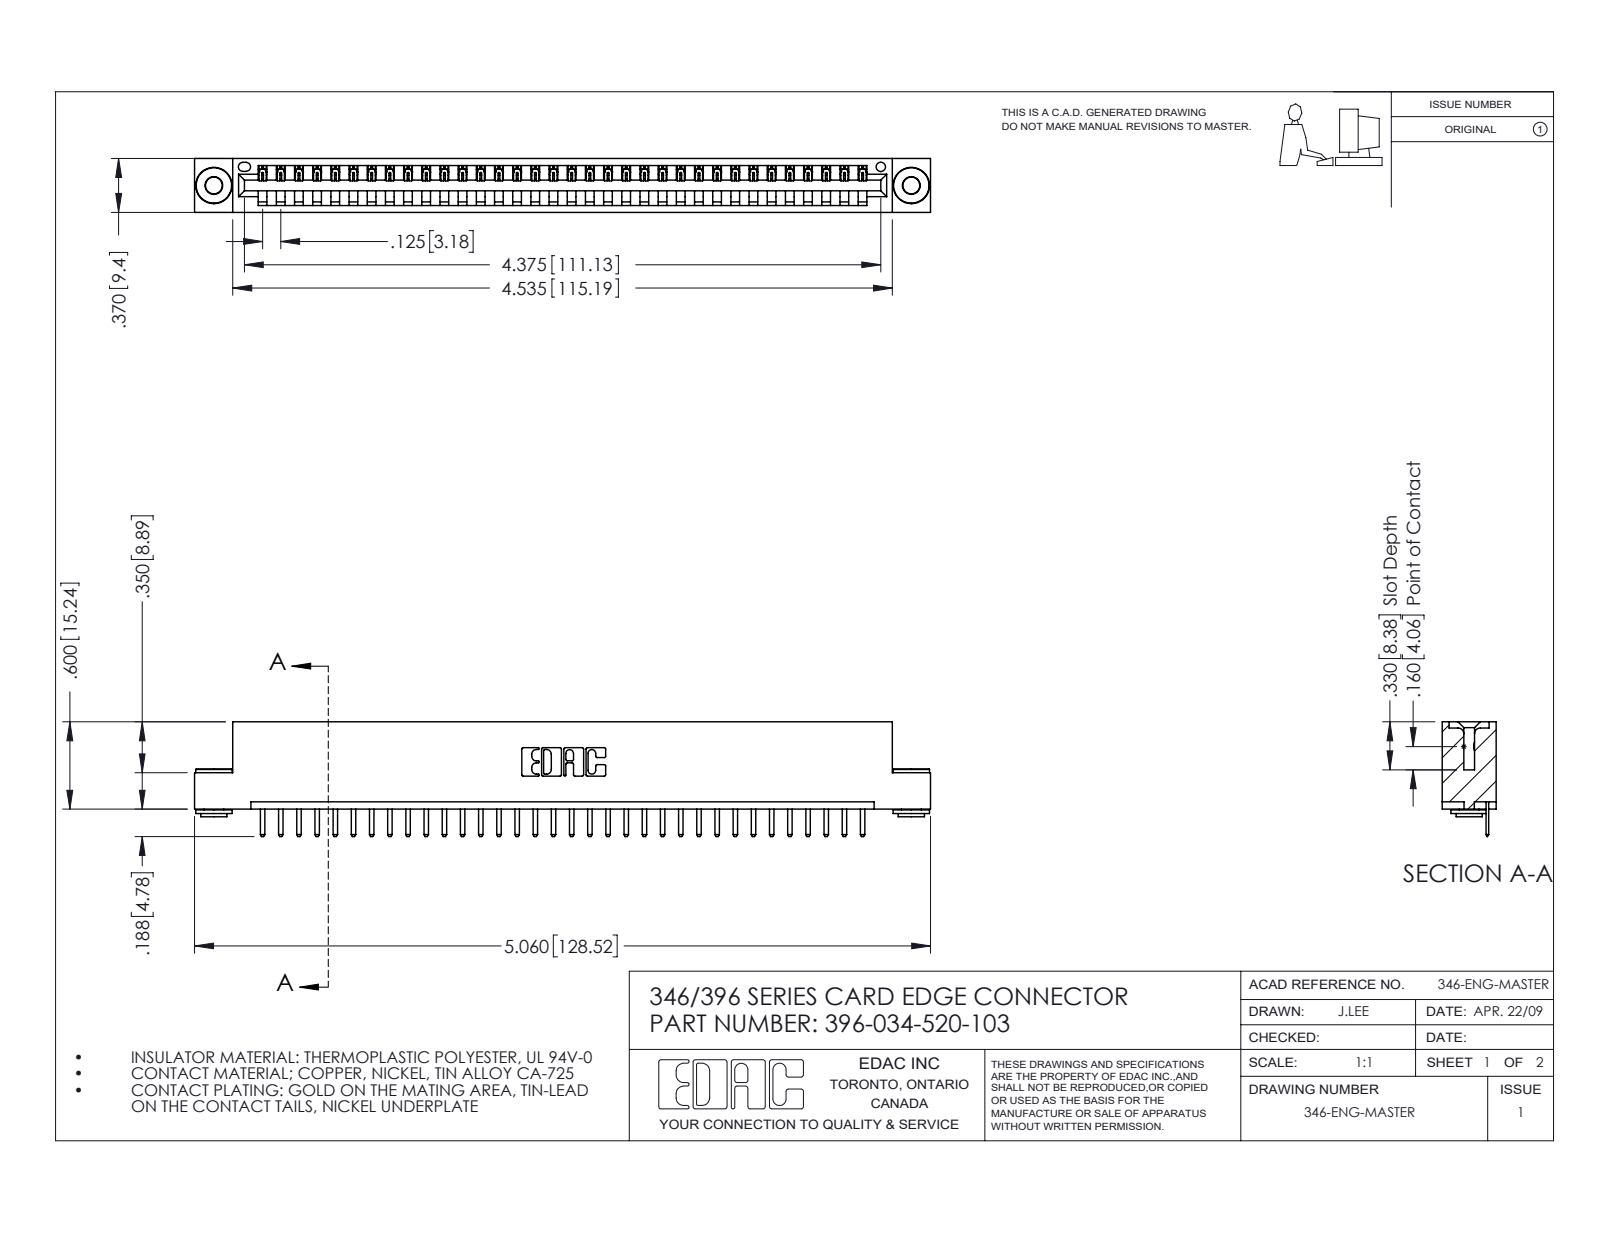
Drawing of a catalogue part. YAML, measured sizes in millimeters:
part_name: "345-292-001_345-293-120; 345-250-002_345-250-002-102; 396-034-520-103; 346 Part_Flush Mounting Lugs - 0.156 Dia-TH"
step_written_by: "SolidWorks 2016 (CONFIG_CONTROL_DESIGN)"
units: millimeters
bodies: {solids: 37, faces: 2268, planar: 1514, cylindrical: 746, other: 8}
overall_size: [128.5, 20, 9.4]
volume: 12200
surface_area: 15020
round_holes:
  - {diameter: 2.9, count: 2}
  - {diameter: 4, count: 2}
  - {diameter: 1.6, count: 1}
round_bosses_or_shafts:
  - {diameter: 6.4, count: 2}
  - {diameter: 4.6, count: 2}
  - {diameter: 3.5, count: 2}
partial_cylinders:
  - {radius: 0.3, count: 70}
  - {radius: 0.2, count: 68}
  - {radius: 0.3, count: 22}
  - {radius: 0.2, count: 6}
  - {radius: 0.8, count: 6}
  - {radius: 0.7, count: 3}
  - {radius: 0.8, count: 2}
  - {radius: 1, count: 2}
face_to_face_distances: [1.2, 8.2, 9.4, 6.4, 3.8, 5.6, 2.5, 4.4, 0.6, 1.8]
hole_center_spacings: [6.2, 116.5, 121.8]
